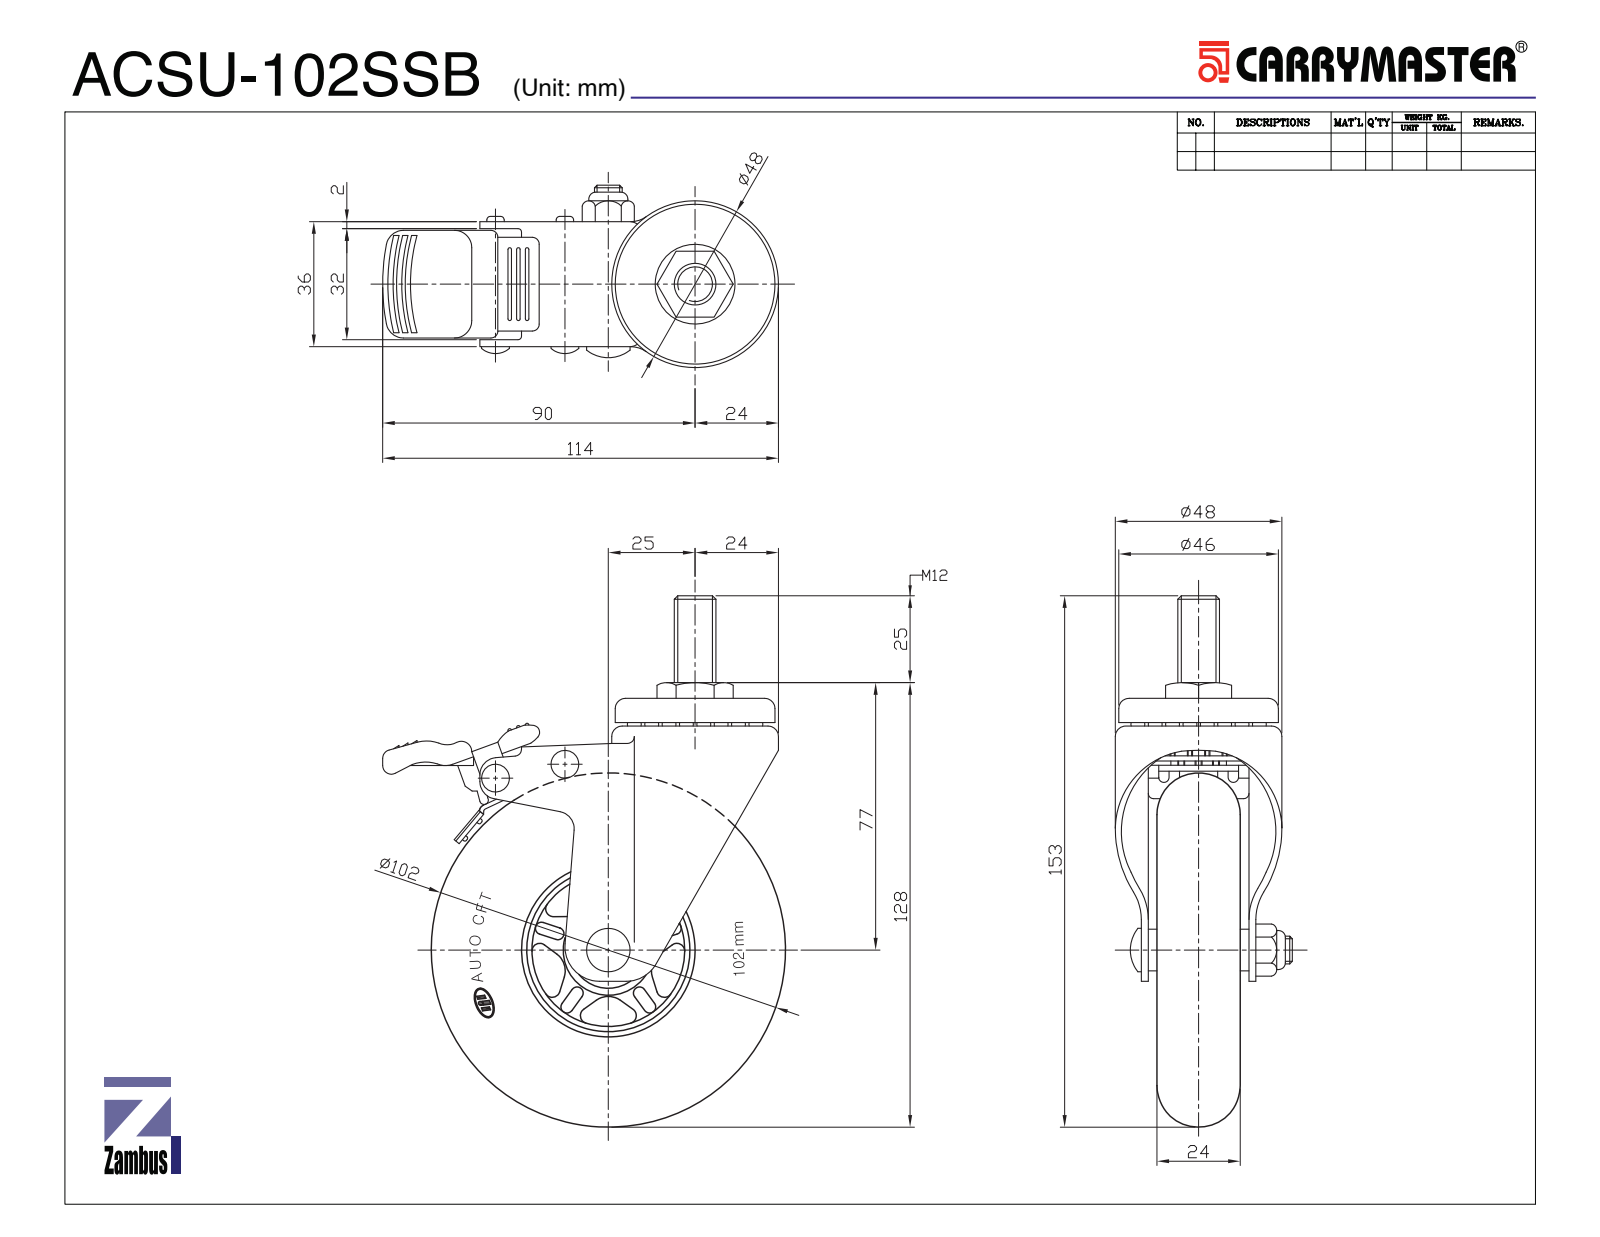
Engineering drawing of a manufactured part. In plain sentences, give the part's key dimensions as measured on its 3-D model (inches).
The part is named "ACSU-102SSB". Its 3-D file was written by "SolidWorks 2015 (CONFIG_CONTROL_DESIGN)". It is 29 solids with 989 faces: 369 planar, 387 cylindrical and 233 other. Overall it measures 6.091 by 4.574 by 1.937 inches. Its volume is 13.35 cubic inches and its surface area 146.1 square inches. Round holes: 2 of diameter 0.138, 2 of diameter 0.157, 1 of diameter 0.268, 1 of diameter 0.315, 1 of diameter 0.319, 1 of diameter 0.433, 1 of diameter 0.469, 1 of diameter 0.709, 1 of diameter 0.728, 1 of diameter 0.866, 1 of diameter 1.035, 1 of diameter 1.543. Round bosses or shafts: 2 of diameter 0.193, 1 of diameter 1.669, 1 of diameter 1.193, 1 of diameter 0.709, 1 of diameter 0.705, 1 of diameter 0.63, 1 of diameter 0.492, 1 of diameter 0.472. Partial cylindrical surfaces (rounded edges, fillets, slot ends): 45 of radius 0.039, 20 of radius 0.024, 14 of radius 0.059, 13 of radius 0.079, 12 of radius 0.067, 8 of radius 0.118, 6 of radius 0.02, 5 of radius 0.098. The main face-to-face distances are 0.079, 0.256, 0.177, 1.201, 1.378, 1.122, 0.945, 0.138, 0.059, 1.457. The hole center spacings are 0.811, 2.16, 2.341.
